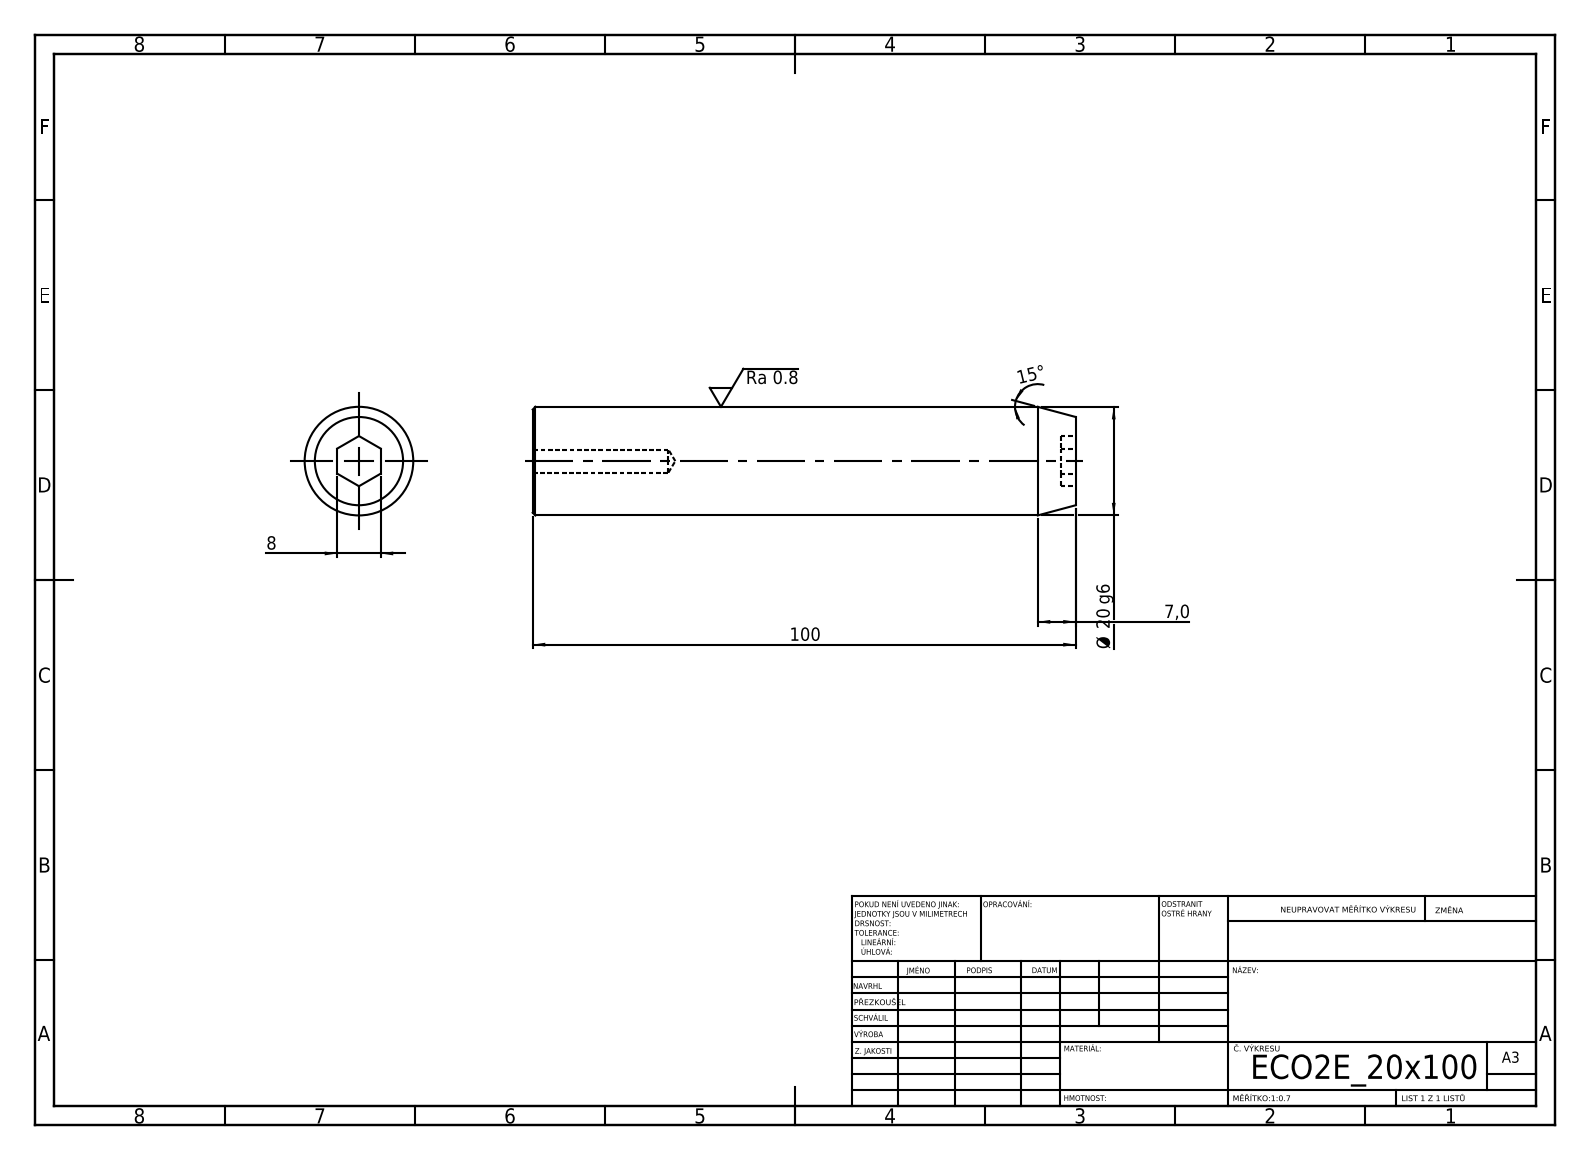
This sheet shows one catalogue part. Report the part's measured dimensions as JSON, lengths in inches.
{"step_written_by": "SolidWorks 2019 (CONFIG_CONTROL_DESIGN)", "units": "inches", "bodies": {"solids": 1, "faces": 19, "planar": 9, "cylindrical": 4, "other": 6}, "overall_size": [3.937, 0.787, 0.787], "volume_in3": 1.862, "surface_area_in2": 11.11, "round_holes": [[0.165, 1]], "round_bosses_or_shafts": [[0.787, 1]], "face_to_face_distances": [3.937, 0.11, 3.827, 0.315]}
